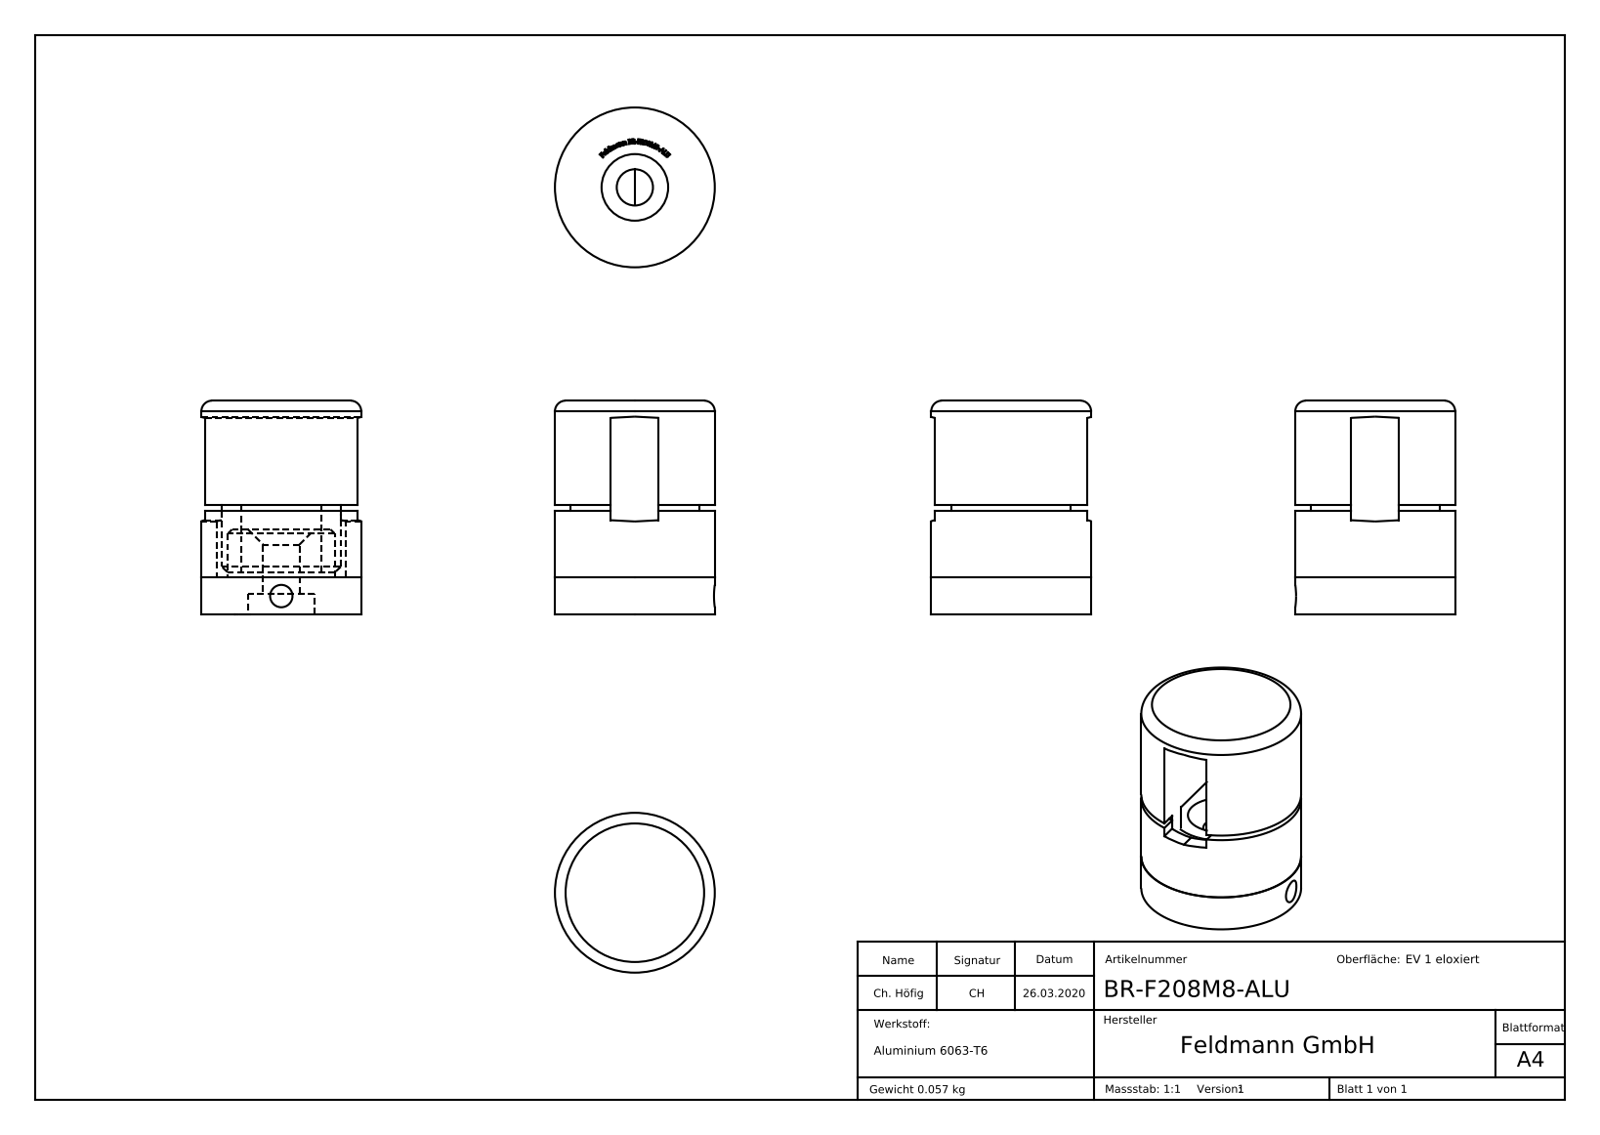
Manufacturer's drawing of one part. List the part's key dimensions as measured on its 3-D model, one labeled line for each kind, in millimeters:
Part name (STEP PRODUCT): BR-R1XM8-XXX Teil3_BR-F208M8-ALU Teil3; BR-R1XM8-XXX Teil3; BR-R1XM8-XXX Teil1_BR-FXXXM8-ALU Teil1; BR-R1XM8-XXX Teil2 (+3 more)
STEP written by: SolidWorks 2015 (CONFIG_CONTROL_DESIGN)
Units: millimetres
Bodies: 3 solids, 329 faces (194 planar, 12 cylindrical, 123 other)
Overall size (bounding box): 64.34 × 30 × 30
Volume: 20 976 mm³ · Surface area: 10 702 mm²
Round holes (diameter × count): ⌀4.2 ×1, ⌀6.8 ×1, ⌀12.5 ×1, ⌀24.2 ×1
Round bosses / shafts (diameter × count): ⌀30 ×1, ⌀20 ×1
Partial cylindrical surfaces — rounded edges, fillets, slot ends (radius × count): R8.75 ×1, R12.05 ×1
Main face-to-face distances: 9, 7, 40.18, 33.18, 1, 12.53, 20.53, 13.53, 19.65, 8
